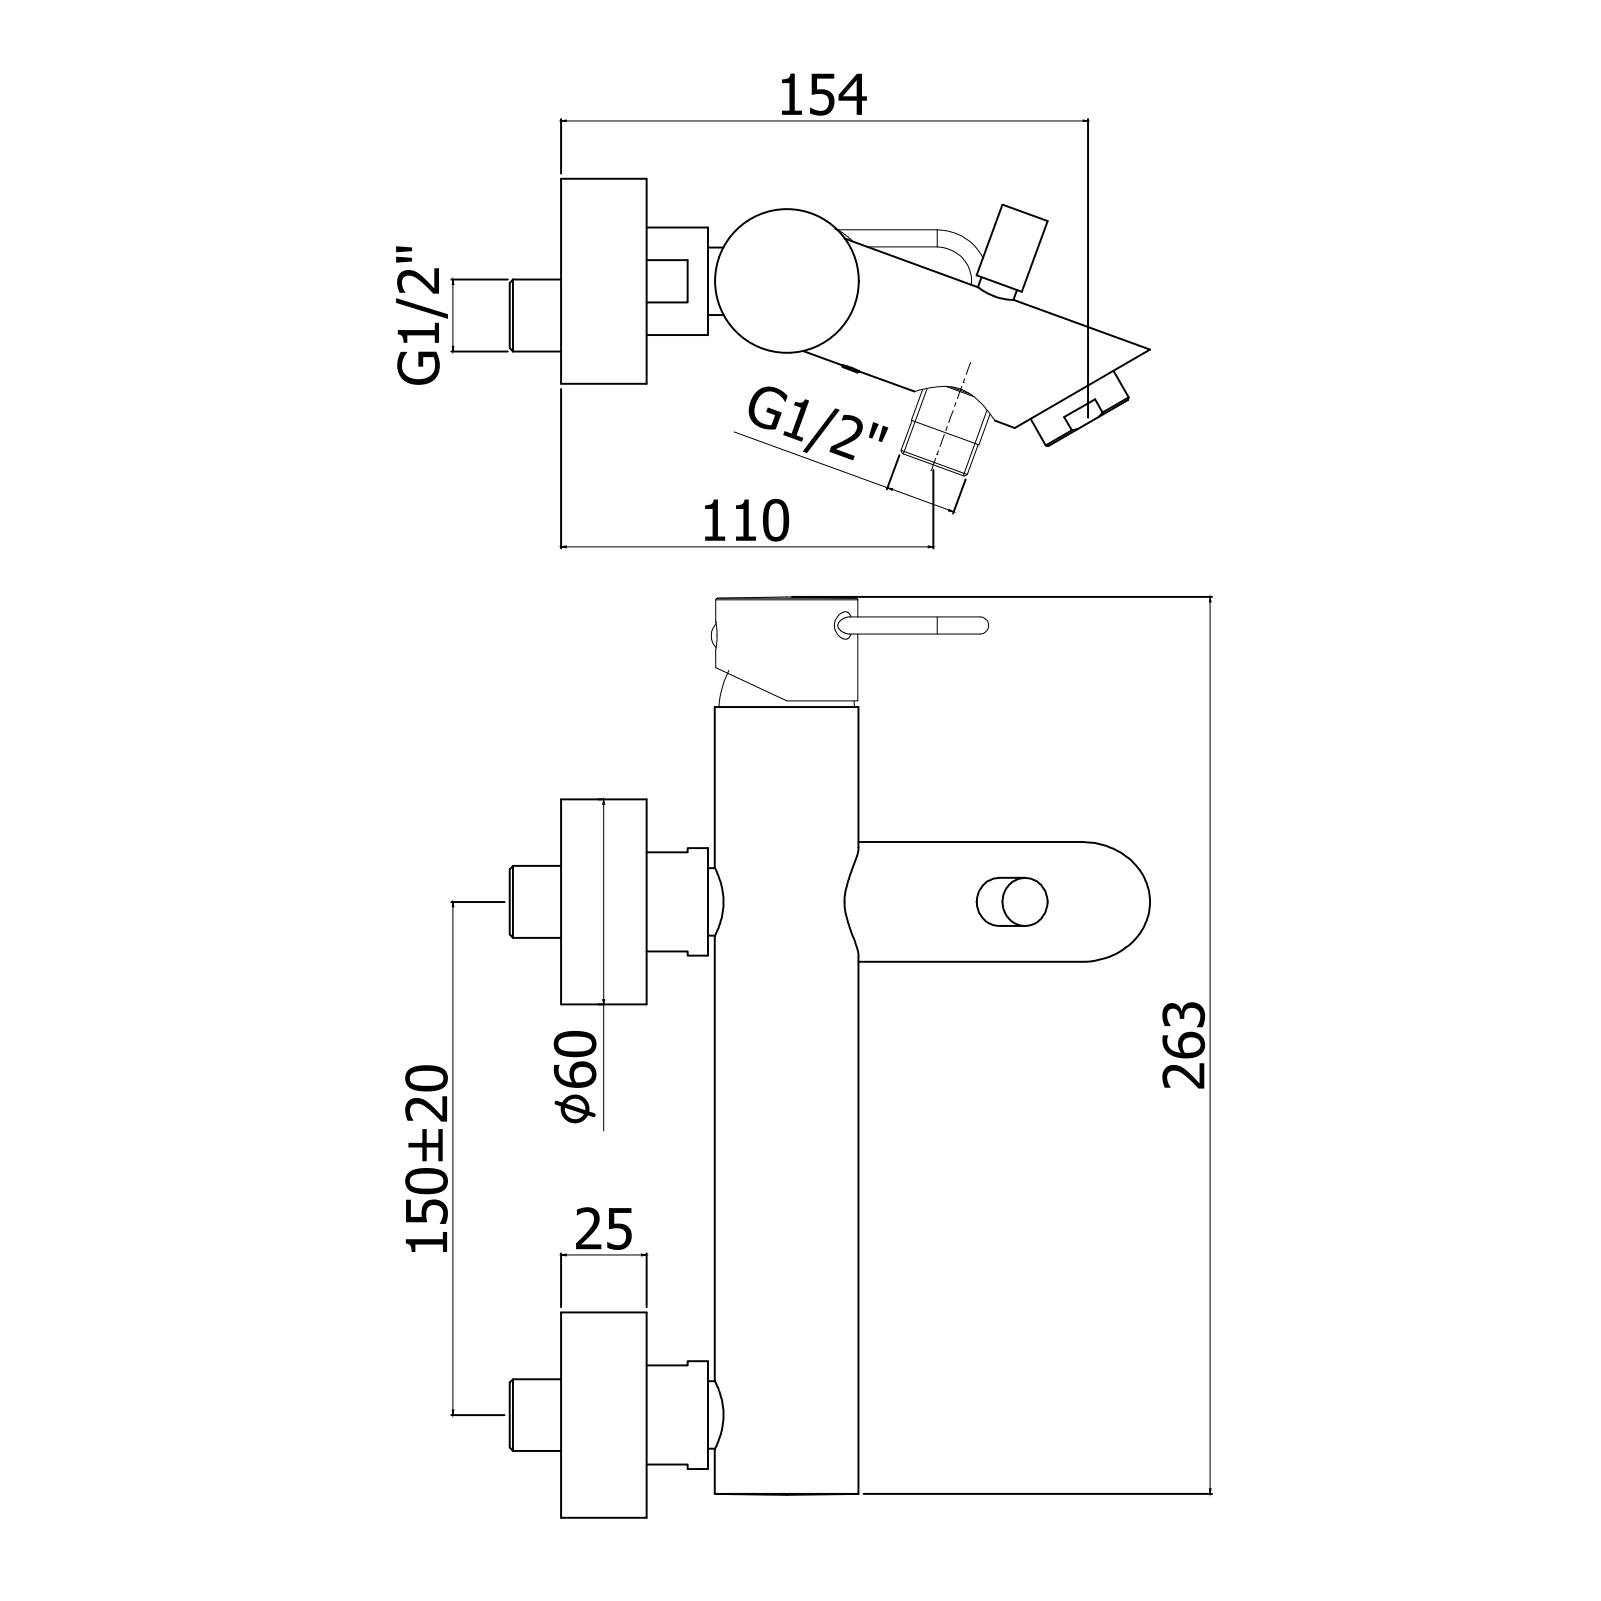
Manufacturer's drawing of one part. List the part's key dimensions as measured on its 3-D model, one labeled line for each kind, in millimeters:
Part name (STEP PRODUCT): JK022CR
STEP written by: CREO PARAMETRIC BY PTC INC, 2020044 (CONFIG_CONTROL_DESIGN)
Units: millimetres
Bodies: 3 solids, 2971 faces (2207 planar, 460 cylindrical, 304 other)
Overall size (bounding box): 269.01 × 171.48 × 86.62
Volume: 411 144 mm³ · Surface area: 148 032 mm²
Round holes (diameter × count): ⌀7.5 ×6, ⌀5 ×5, ⌀12 ×5, ⌀8 ×3, ⌀9 ×3, ⌀16 ×3, ⌀18 ×3, ⌀24.5 ×3, ⌀4 ×2, ⌀10.5 ×2, ⌀16.7 ×2, ⌀20 ×2
Round bosses / shafts (diameter × count): ⌀5 ×5, ⌀24 ×3, ⌀59.7 ×2, ⌀35 ×2, ⌀31.5 ×2, ⌀20.6 ×2, ⌀19.7 ×2, ⌀41.5 ×1
Partial cylindrical surfaces — rounded edges, fillets, slot ends (radius × count): R0.5 ×44, R0.15 ×11, R0.3 ×9, R1 ×4, R7 ×4, R1.56 ×2, R4.5 ×2, R7.95 ×2
Main face-to-face distances: 5, 2.5, 3, 10, 1, 18, 23, 0.5, 25, 9
Hole centre spacings: 6.13, 6, 0.71, 1.25, 2.64, 6.16, 8.51, 8.6
